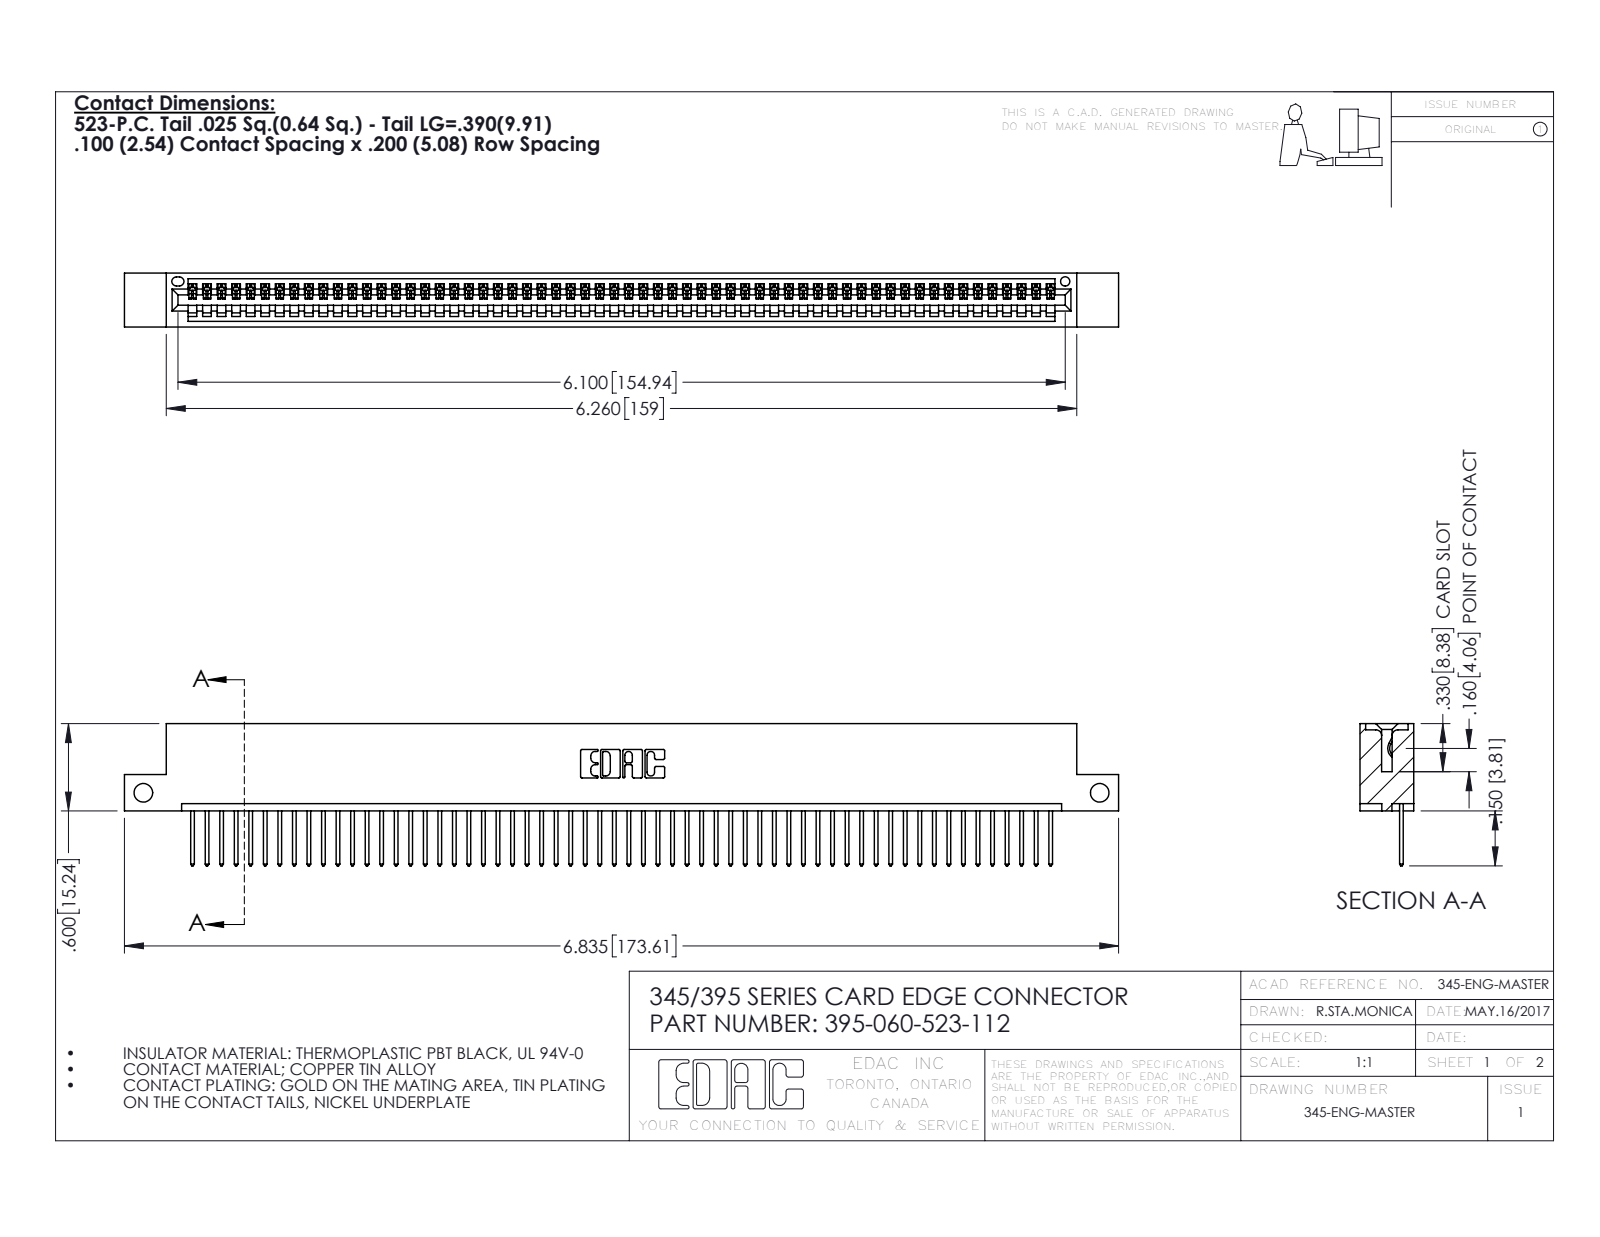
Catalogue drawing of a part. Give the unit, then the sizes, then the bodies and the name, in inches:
Units: inches
Overall size (bounding box): 6.835 × 0.977 × 0.37
Round holes (diameter × count): ⌀0.128 ×2, ⌀0.064 ×1
Partial cylindrical surfaces — rounded edges, fillets, slot ends (radius × count): R0.006 ×120, R0.01 ×120, R0.01 ×22, R0.007 ×6, R0.031 ×6, R0.026 ×3, R0.031 ×2, R0.04 ×2
Main face-to-face distances: 0.298, 0.072, 0.37, 0.2, 0.098, 0.272, 0.025, 0.225, 0.149, 0.072
Hole centre spacings: 6.575
Volume: 1.009 in³ · Surface area: 34.3 in²
Bodies: 61 solids, 3606 faces (2480 planar, 1126 cylindrical, 0 other)
Part name (STEP PRODUCT): 345 Part_Flush Mounting Lugs - Side Mount; 395-060-523-112; 345-292-001_345-293-123
STEP written by: SolidWorks 2016 (CONFIG_CONTROL_DESIGN)
